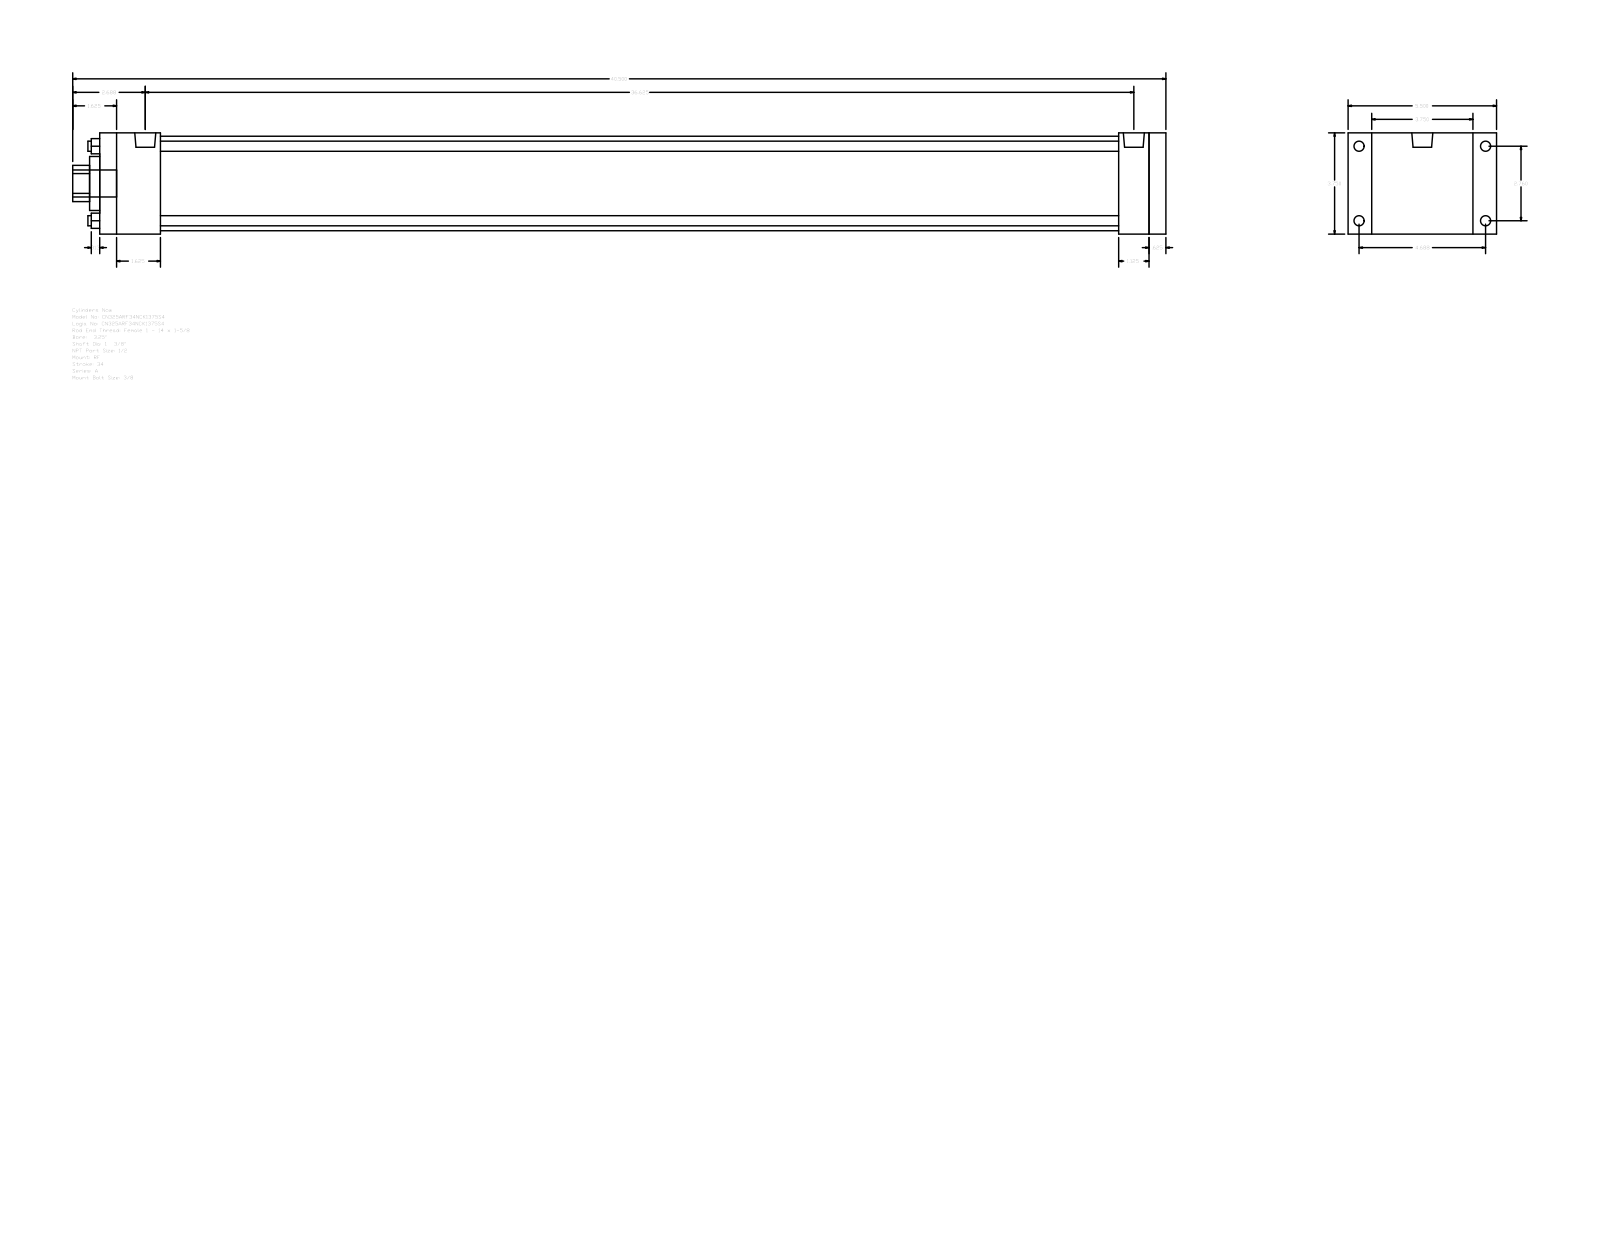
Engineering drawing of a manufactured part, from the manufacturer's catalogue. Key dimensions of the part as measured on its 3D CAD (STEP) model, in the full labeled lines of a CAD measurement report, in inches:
Part name (STEP PRODUCT): A_RF__0325_1.375
STEP written by: GSSL Pune (CONFIG_CONTROL_DESIGN)
Units: inches
Bodies: 0 solids, 92 faces (64 planar, 28 cylindrical, 0 other)
Overall size (bounding box): 40.5 × 5.5 × 3.75
Round holes (diameter × count): ⌀0.375 ×4, ⌀1.375 ×1, ⌀2 ×1, ⌀3.5 ×1
Round bosses / shafts (diameter × count): ⌀0.375 ×4, ⌀0.344 ×4, ⌀0.778 ×2, ⌀1 ×1
Partial cylindrical surfaces — rounded edges, fillets, slot ends (radius × count): R0.672 ×1
Main face-to-face distances: 3.75, 39.5, 0.625, 38.875, 1.125, 0.875, 4.625, 37.75, 1.75, 2.25
Hole centre spacings: 1.952, 2.76, 3.903
